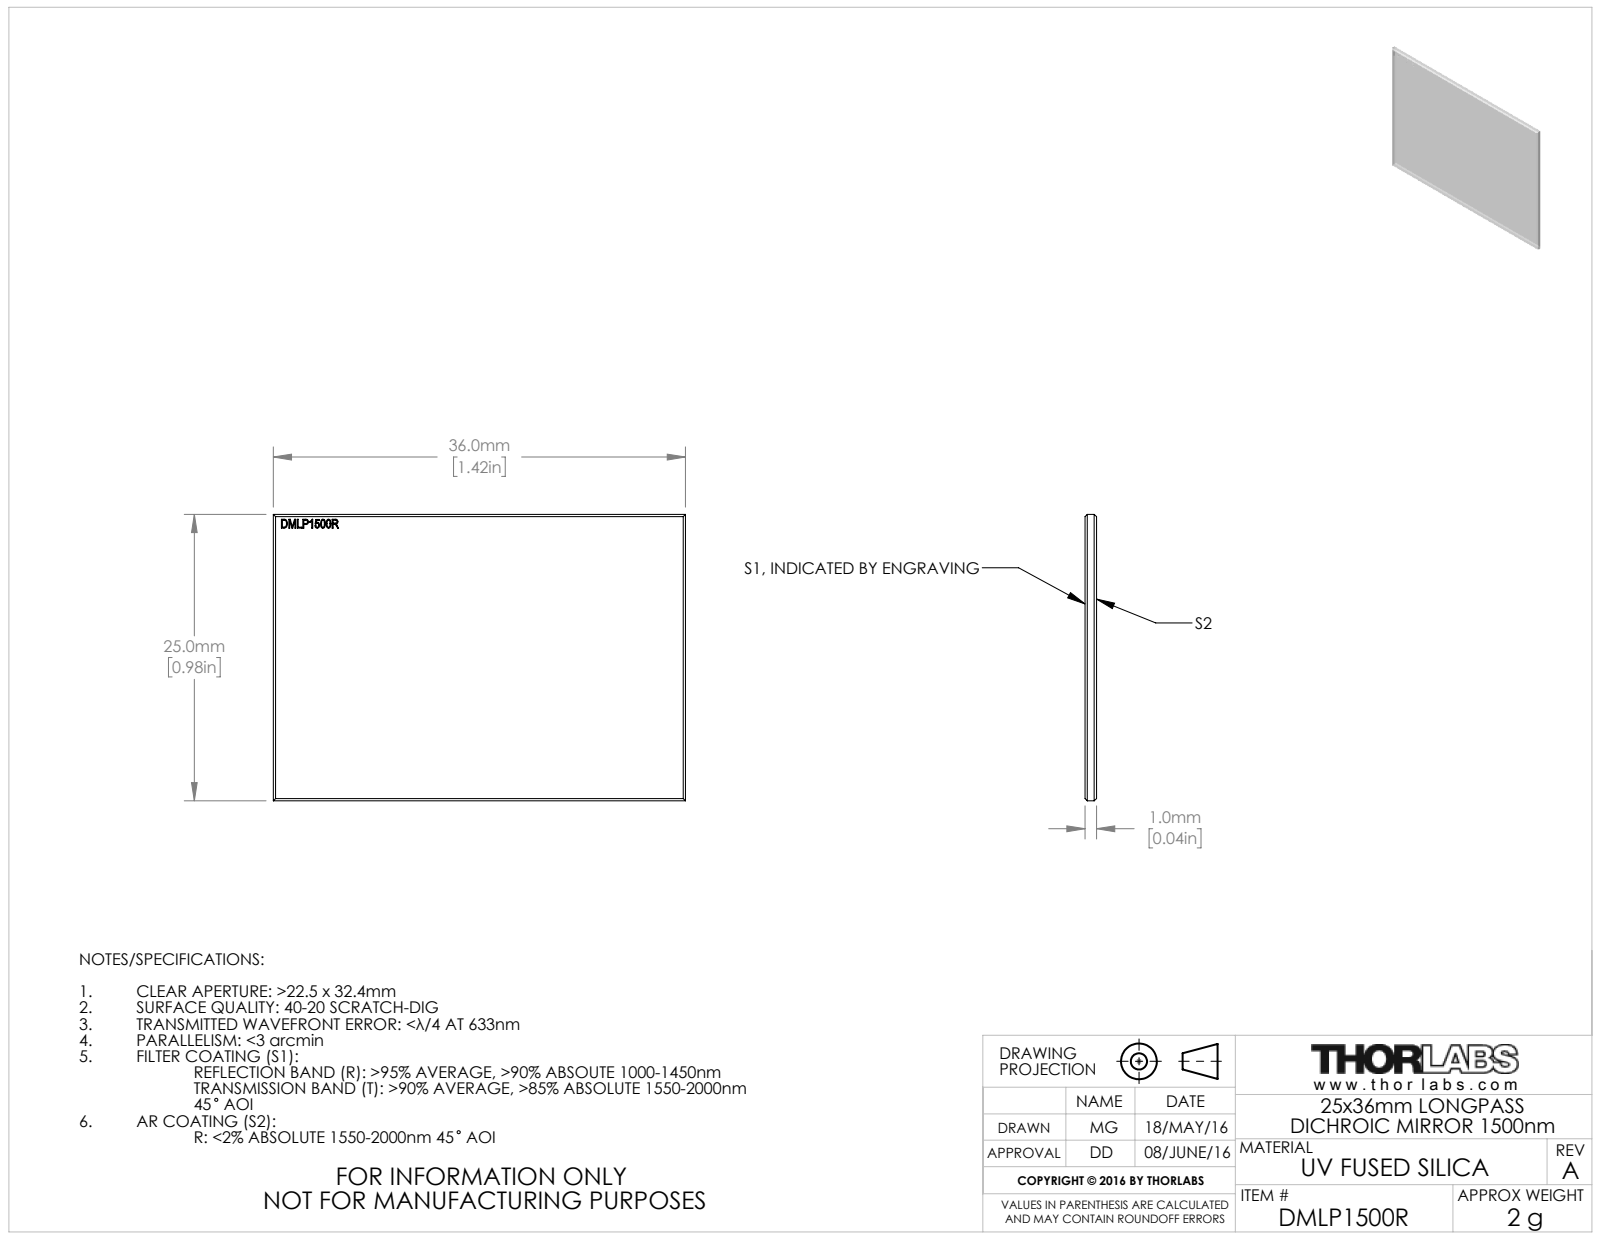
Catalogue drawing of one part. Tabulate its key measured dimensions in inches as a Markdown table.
| quantity | value |
| --- | --- |
| part name | TTN045189-E0W |
| STEP written by | SolidWorks 2016 (CONFIG_CONTROL_DESIGN) |
| units | inches |
| bodies | 1 solid, 133 faces (85 planar, 0 cylindrical, 48 other) |
| overall size | 1.417 × 0.984 × 0.039 |
| volume | 0.055 in³ |
| surface area | 2.936 in² |
| main face-to-face distances | 0.039, 0.984, 0.713, 1.417, 1.019, 0.039, 0.03, 0.021, 0.048, 0.028 |
